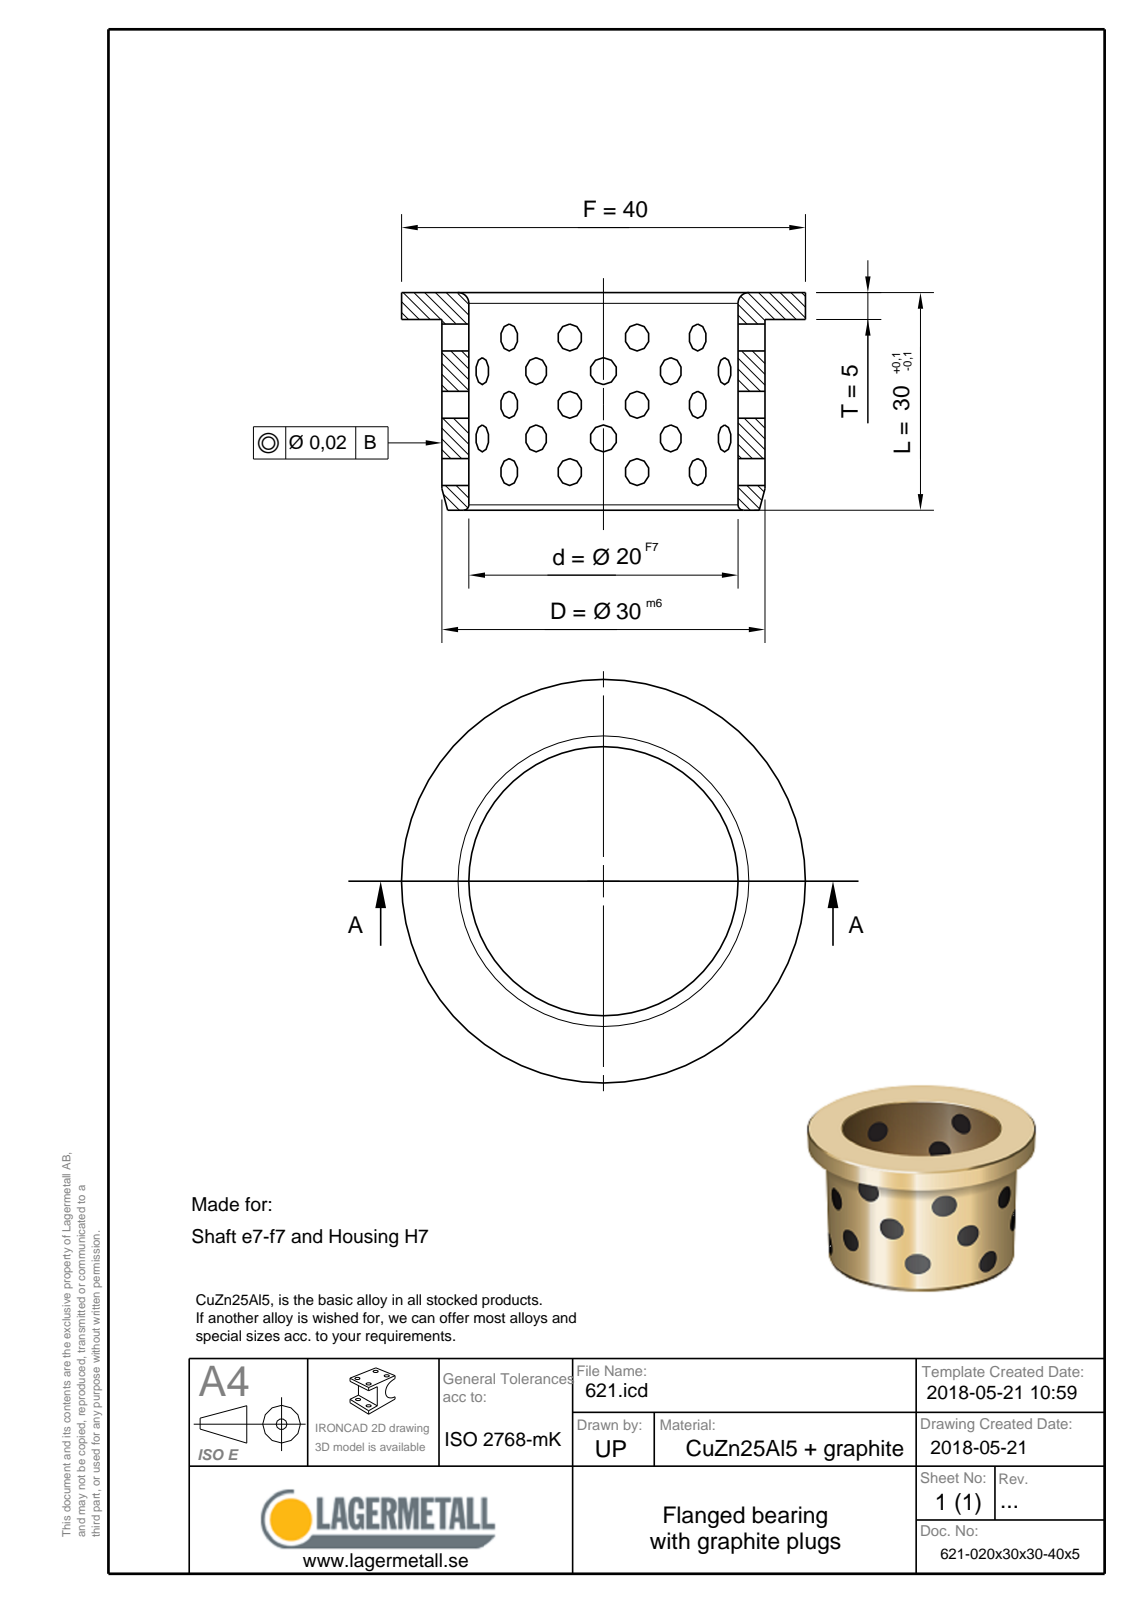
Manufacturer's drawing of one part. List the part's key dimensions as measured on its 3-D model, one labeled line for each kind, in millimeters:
Part name (STEP PRODUCT): 621-020x30x30-40x5
STEP written by: Spatial InterOp 3D (CONFIG_CONTROL_DESIGN)
Units: millimetres
Bodies: 1 solid, 9 faces (3 planar, 3 cylindrical, 3 other)
Overall size (bounding box): 40 × 40 × 30
Volume: 14 398 mm³ · Surface area: 6 613 mm²
Round holes (diameter × count): ⌀20 ×1
Round bosses / shafts (diameter × count): ⌀40 ×1, ⌀30 ×1
Main face-to-face distances: 5, 25, 30
